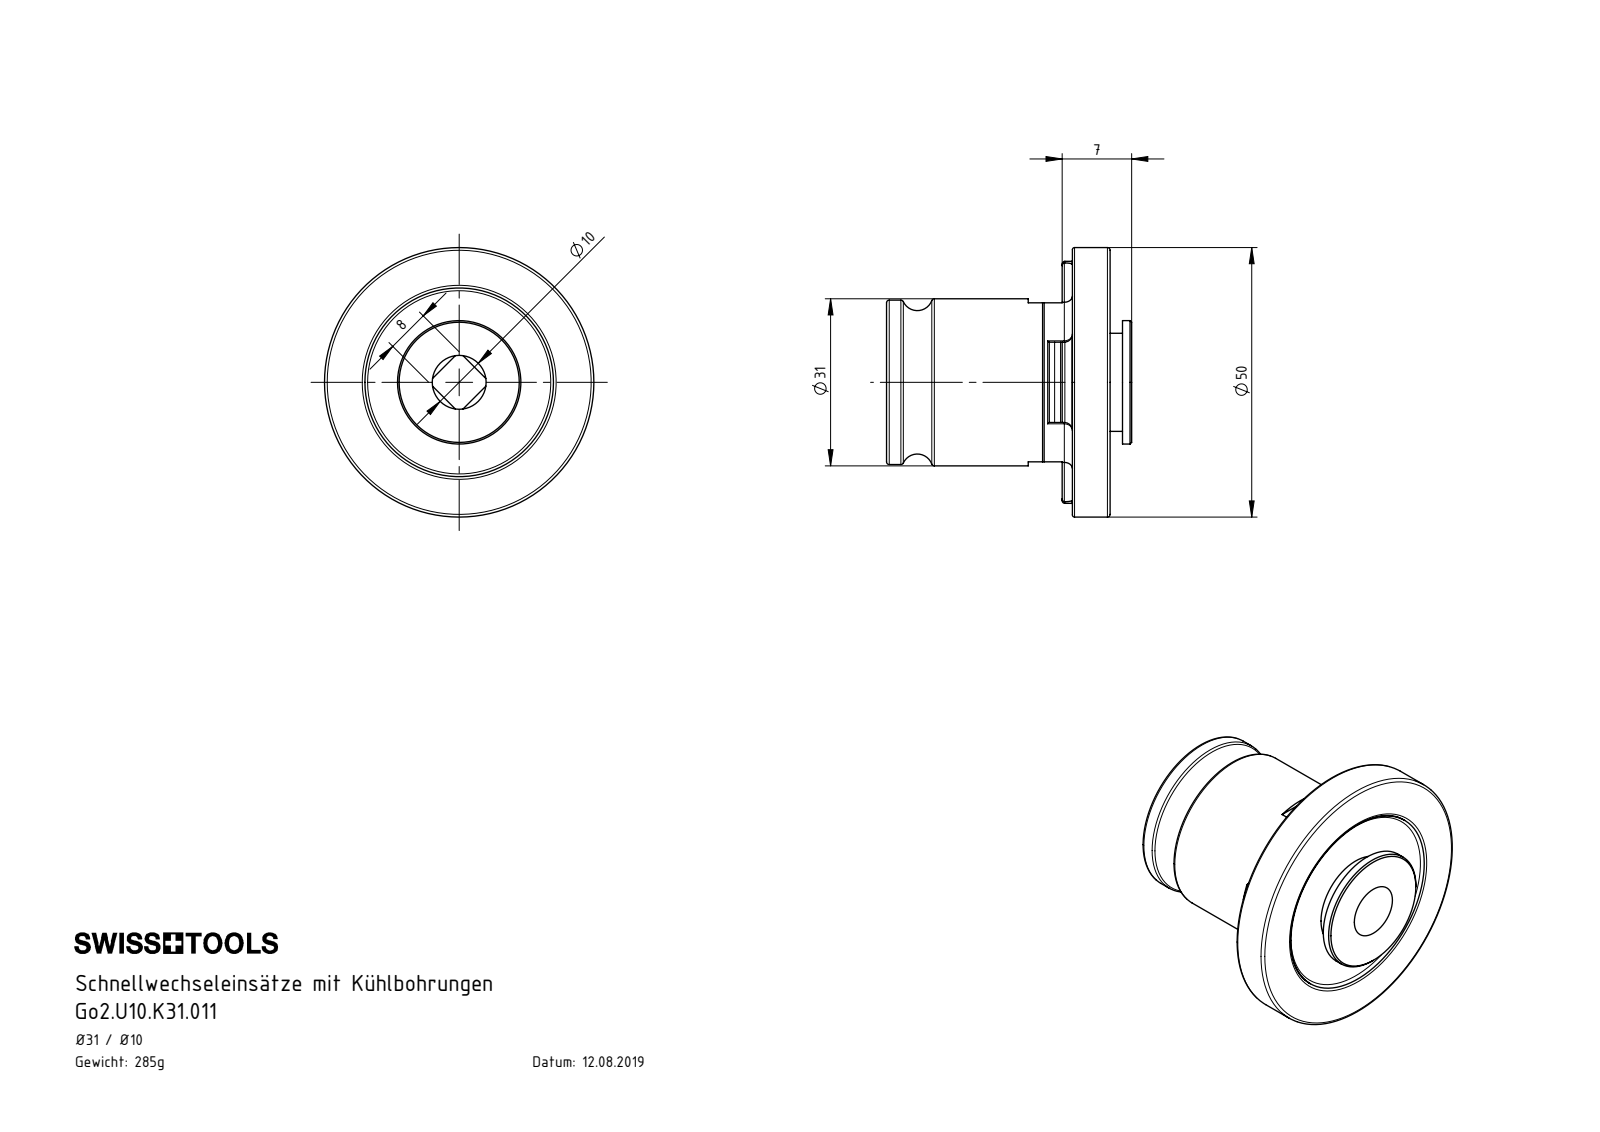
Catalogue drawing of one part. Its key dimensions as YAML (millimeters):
part_name: "Go2.U10.K31.011"
step_written_by: "SolidWorks 2017 (AUTOMOTIVE_DESIGN)"
units: millimeters
bodies: {solids: 1, faces: 102, planar: 37, cylindrical: 28, other: 37}
overall_size: [50, 50, 45.5]
volume: 36333
surface_area: 10524
round_holes:
  - {diameter: 10, count: 1}
  - {diameter: 20.1, count: 1}
round_bosses_or_shafts:
  - {diameter: 50, count: 1}
  - {diameter: 35, count: 1}
  - {diameter: 31, count: 1}
  - {diameter: 30.6, count: 1}
  - {diameter: 30.5, count: 1}
  - {diameter: 22.9, count: 1}
  - {diameter: 18.2, count: 1}
partial_cylinders:
  - {radius: 1.5, count: 5}
  - {radius: 0.5, count: 4}
  - {radius: 20, count: 1}
  - {radius: 22.45, count: 1}
face_to_face_distances: [7, 6.35, 0.65, 34.5, 40.85, 41.5, 45.5, 11, 4.65, 4]
